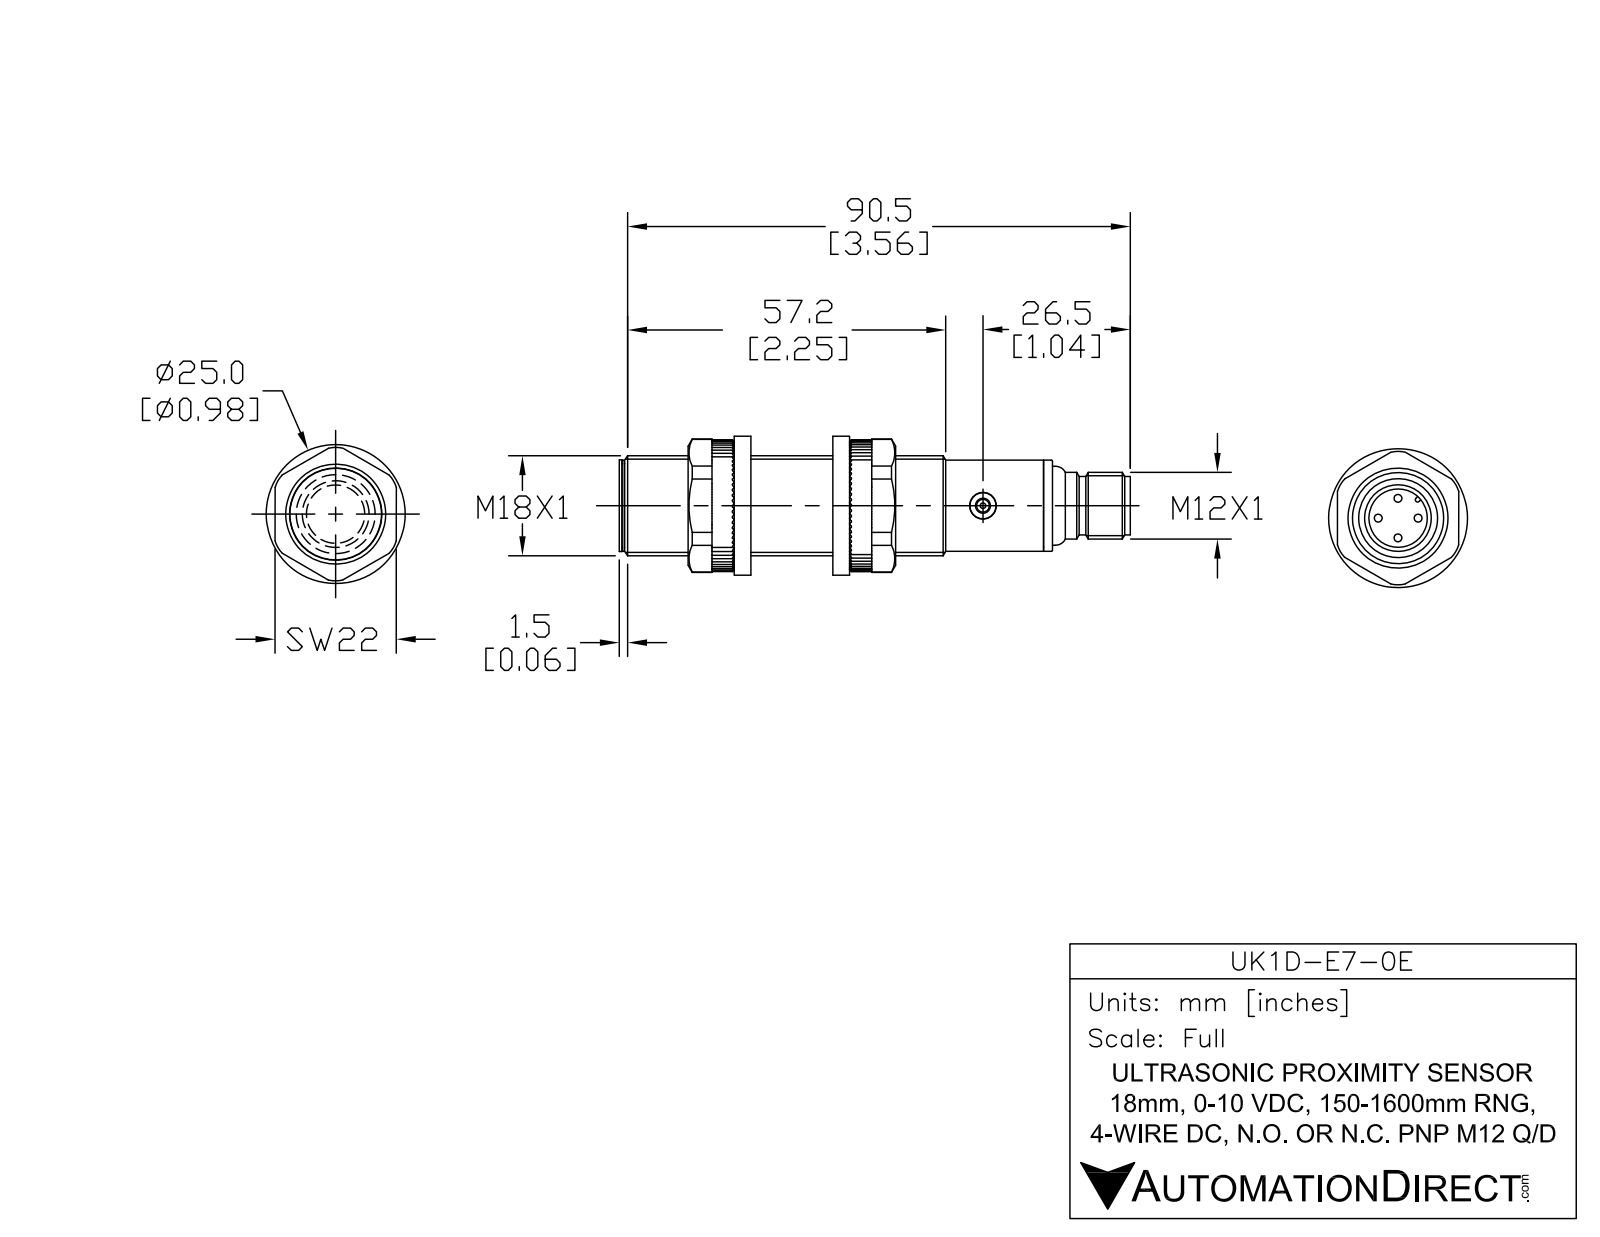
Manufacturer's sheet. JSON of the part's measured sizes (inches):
{"part_name": "UK1D-E7-0E", "step_written_by": "SolidWorks 2017 (AUTOMOTIVE_DESIGN)", "units": "inches", "bodies": {"solids": 6, "faces": 106, "planar": 21, "cylindrical": 48, "other": 37}, "overall_size": [3.606, 0.709, 0.709], "volume_in3": 1.202, "surface_area_in2": 10.68, "round_holes": [[0.106, 1], [0.185, 1], [0.276, 1], [0.327, 1], [0.374, 1]], "round_bosses_or_shafts": [[0.039, 4], [0.709, 1], [0.654, 1], [0.646, 1], [0.622, 1], [0.559, 1], [0.472, 1], [0.413, 1]], "partial_cylinders_radius": [[0.024, 1]], "face_to_face_distances": [2.957, 0.039, 2.996, 0.037, 2.994, 0.043, 0.157, 3.055, 3.053, 3.016]}
